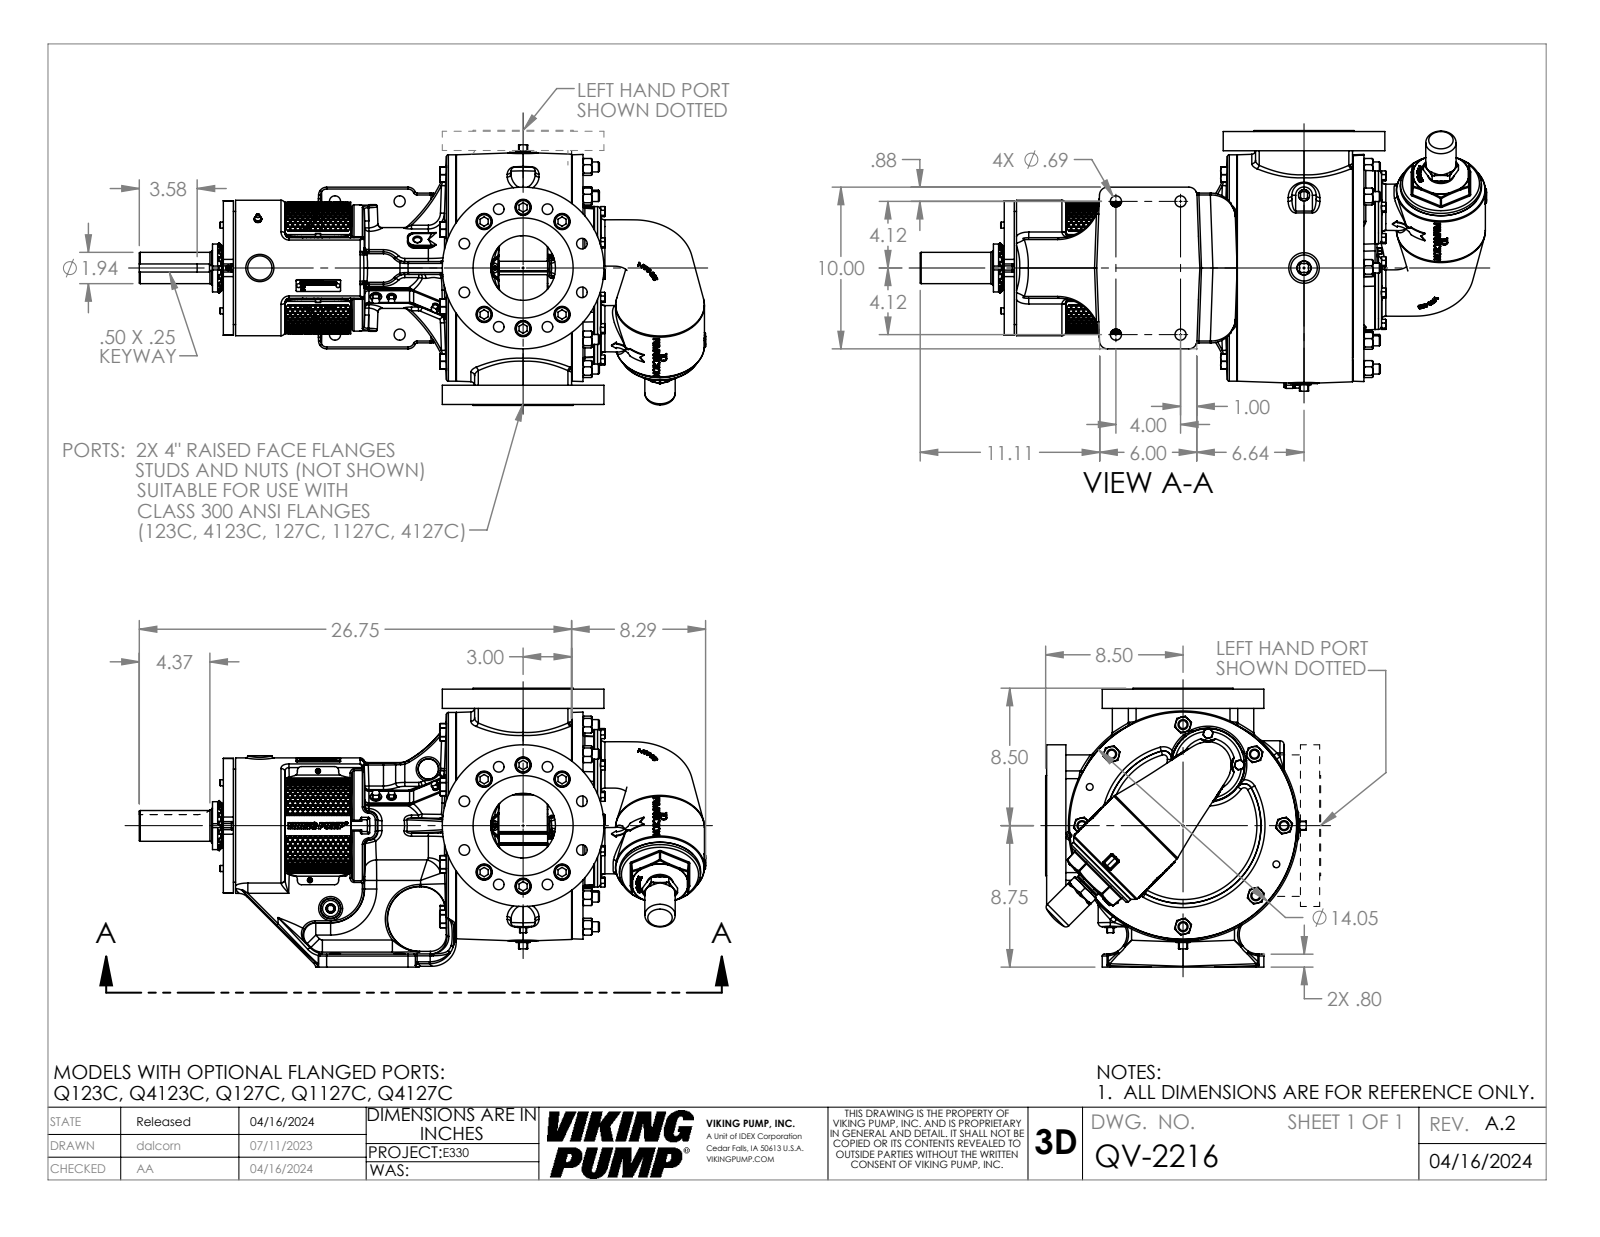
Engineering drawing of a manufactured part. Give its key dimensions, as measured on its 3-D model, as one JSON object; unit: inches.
{"part_name": "QV-2216", "step_written_by": "SolidWorks 2023 (AUTOMOTIVE_DESIGN)", "units": "inches", "bodies": {"solids": 1, "faces": 4901, "planar": 1744, "cylindrical": 852, "other": 2305}, "overall_size": [35.04, 17.25, 16.121], "volume_in3": 2352, "surface_area_in2": 2423, "round_holes": [[0.656, 28], [1, 12], [0.25, 9], [0.266, 8], [0.406, 8], [0.41, 8], [1.157, 8], [0.688, 4], [0.159, 2], [0.313, 2], [0.33, 2], [0.422, 2]], "round_bosses_or_shafts": [[0.937, 12], [0.625, 9], [0.617, 8], [0.375, 8], [0.625, 3], [0.312, 3], [0.19, 3], [10, 2]], "partial_cylinders_radius": [[0.12, 60], [0.06, 34], [0.25, 30], [0.5, 23], [0.015, 18], [0.092, 18], [0.07, 16], [0.75, 16]], "face_to_face_distances": [1.19, 3.75, 16, 1.25, 17.19, 0.5, 0.06, 21.754, 22.254, 18.004], "hole_center_spacings": [3.75, 7.276, 2.079, 3.937, 5.783, 1.184, 2.713, 3.013]}
